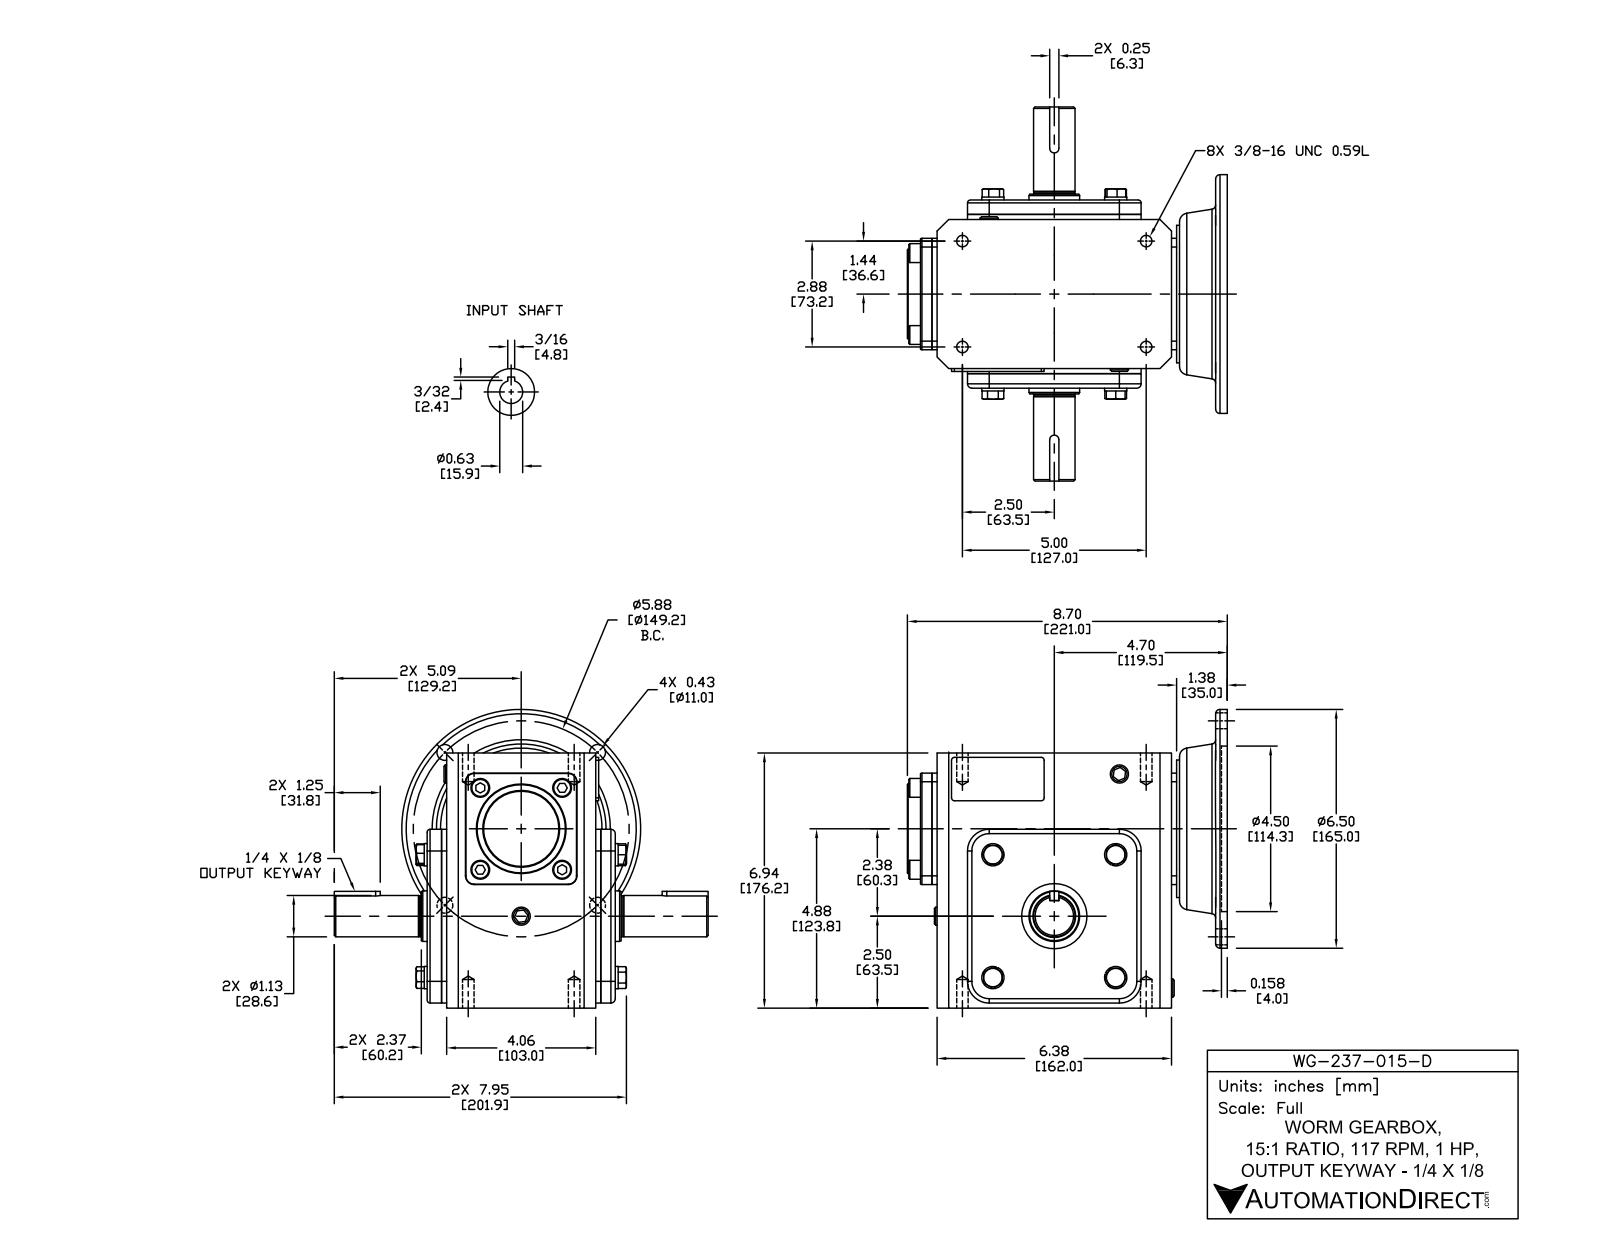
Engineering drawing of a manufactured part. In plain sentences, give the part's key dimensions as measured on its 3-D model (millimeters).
The part is named "WG-237-015-D". Its 3-D file was written by "SolidWorks 2015 (CONFIG_CONTROL_DESIGN)". It is 39 solids with 572 faces: 308 planar, 164 cylindrical and 100 other. Overall it measures 258.4 by 221 by 206.3 millimeters. Its volume is 3 705 000 cubic millimeters and its surface area 339 100 square millimeters. Round holes: 4 of diameter 8, 4 of diameter 10.3, 1 of diameter 15, 1 of diameter 15.9, 1 of diameter 35, 1 of diameter 37, 1 of diameter 45, 1 of diameter 97, 1 of diameter 114.3. Round bosses or shafts: 4 of diameter 15.4, 4 of diameter 13, 1 of diameter 165, 1 of diameter 95, 1 of diameter 62, 1 of diameter 52, 1 of diameter 30, 1 of diameter 29. Partial cylindrical surfaces (rounded edges, fillets, slot ends): 8 of radius 2, 8 of radius 3, 6 of radius 6, 4 of radius 15, 2 of radius 0.5, 2 of radius 1, 2 of radius 3.2. The main face-to-face distances are 3.5, 110, 120, 10, 13.5, 116.5, 106.5, 165.5, 176.2, 8. The hole center spacings are 74.6, 53.3, 73.2, 105.5, 105.5, 124.8, 127, 146.6.
